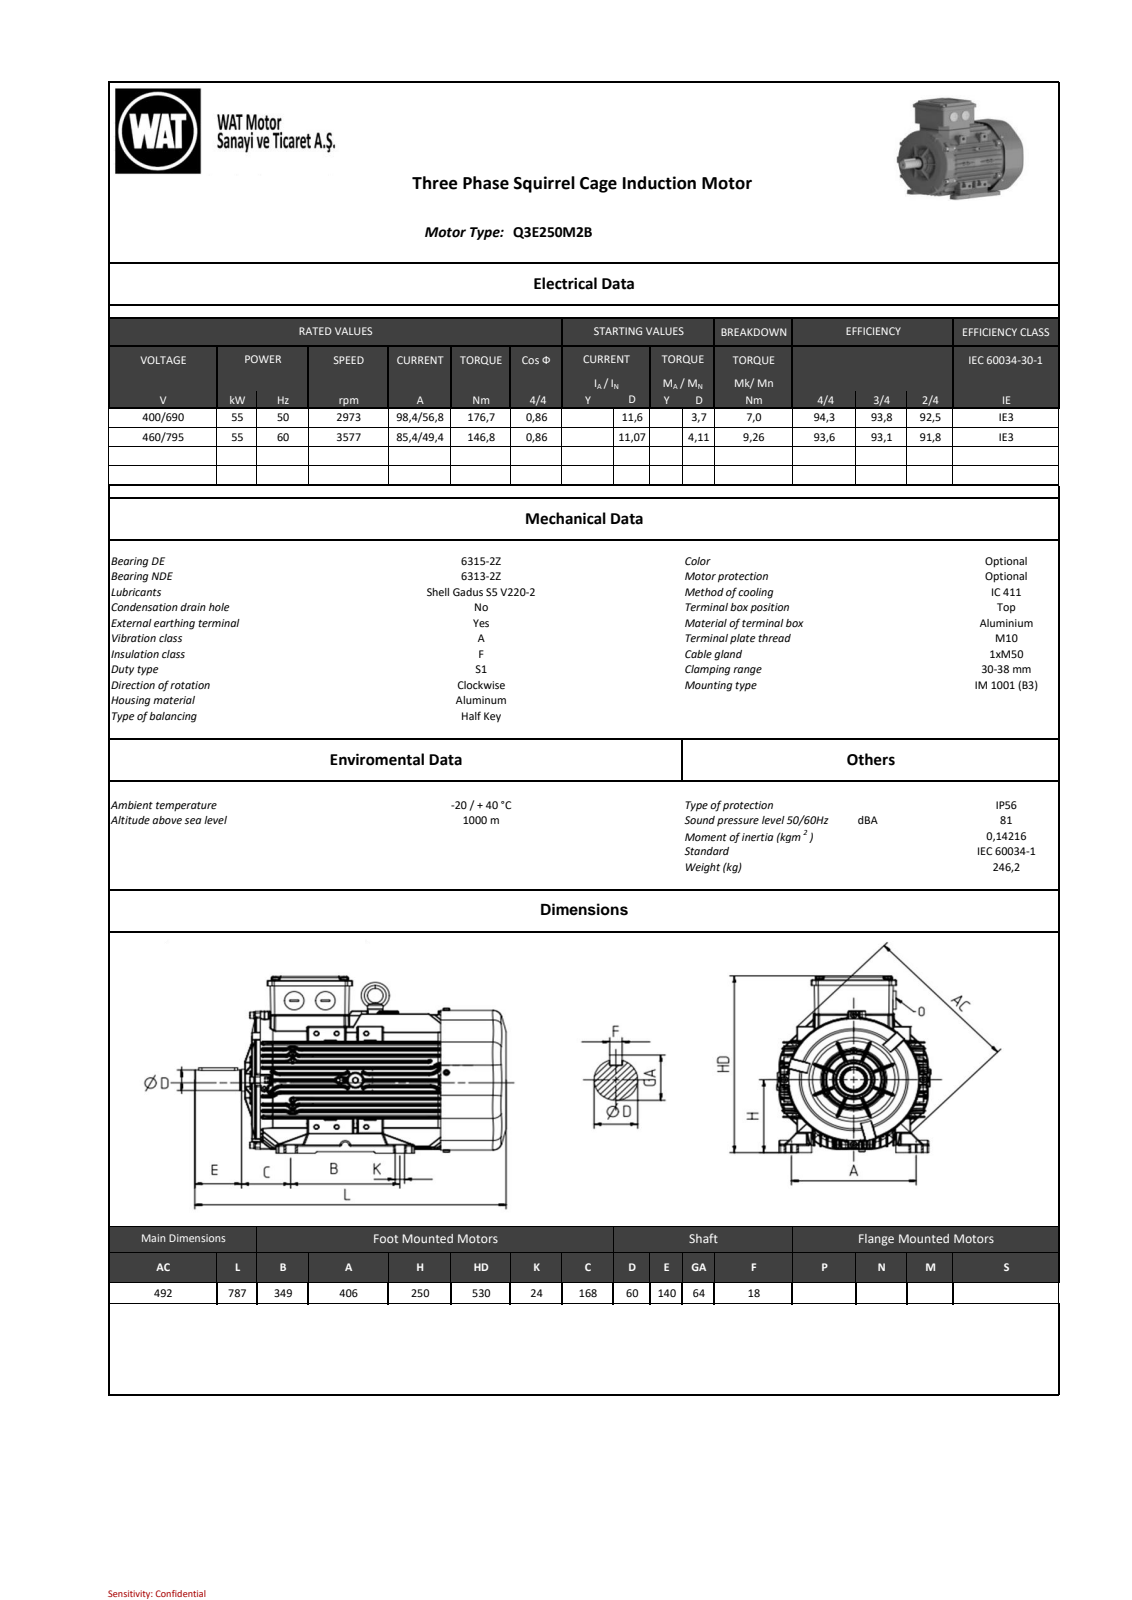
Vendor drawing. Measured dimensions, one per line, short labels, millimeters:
name: 001_objects
written by: SIEMENS PLM Software NX2206.8101 (AUTOMOTIVE_DESIGN)
unit: mm
bodies: 0 solids, 15087 faces (7068 planar, 3869 cylindrical, 4150 other)
size: 787 × 532.5 × 492
holes: 13× ⌀8.5, 12× ⌀9.15, 11× ⌀10.2, 8× ⌀6, 6× ⌀0.7, 5× ⌀5, 5× ⌀7.5, 5× ⌀11, 4× ⌀4.3, 4× ⌀5.5, 4× ⌀6.5, 4× ⌀6.86
bosses: 18× ⌀10, 12× ⌀15.73, 11× ⌀18.1, 6× ⌀8, 4× ⌀14.8, 4× ⌀12.73, 4× ⌀5, 3× ⌀5.85
rounds: 966× R1, 356× R0.2, 312× R2, 274× R0.5, 151× R2.5, 117× R5, 105× R4, 52× R0.3
face distances: 8, 189.81, 5, 15.53, 3, 169.04, 20.77, 14.83, 184.57, 5.24
hole spacings: 7.4, 156, 146.34, 45.26, 68.18, 98.65, 186.17, 192.6
